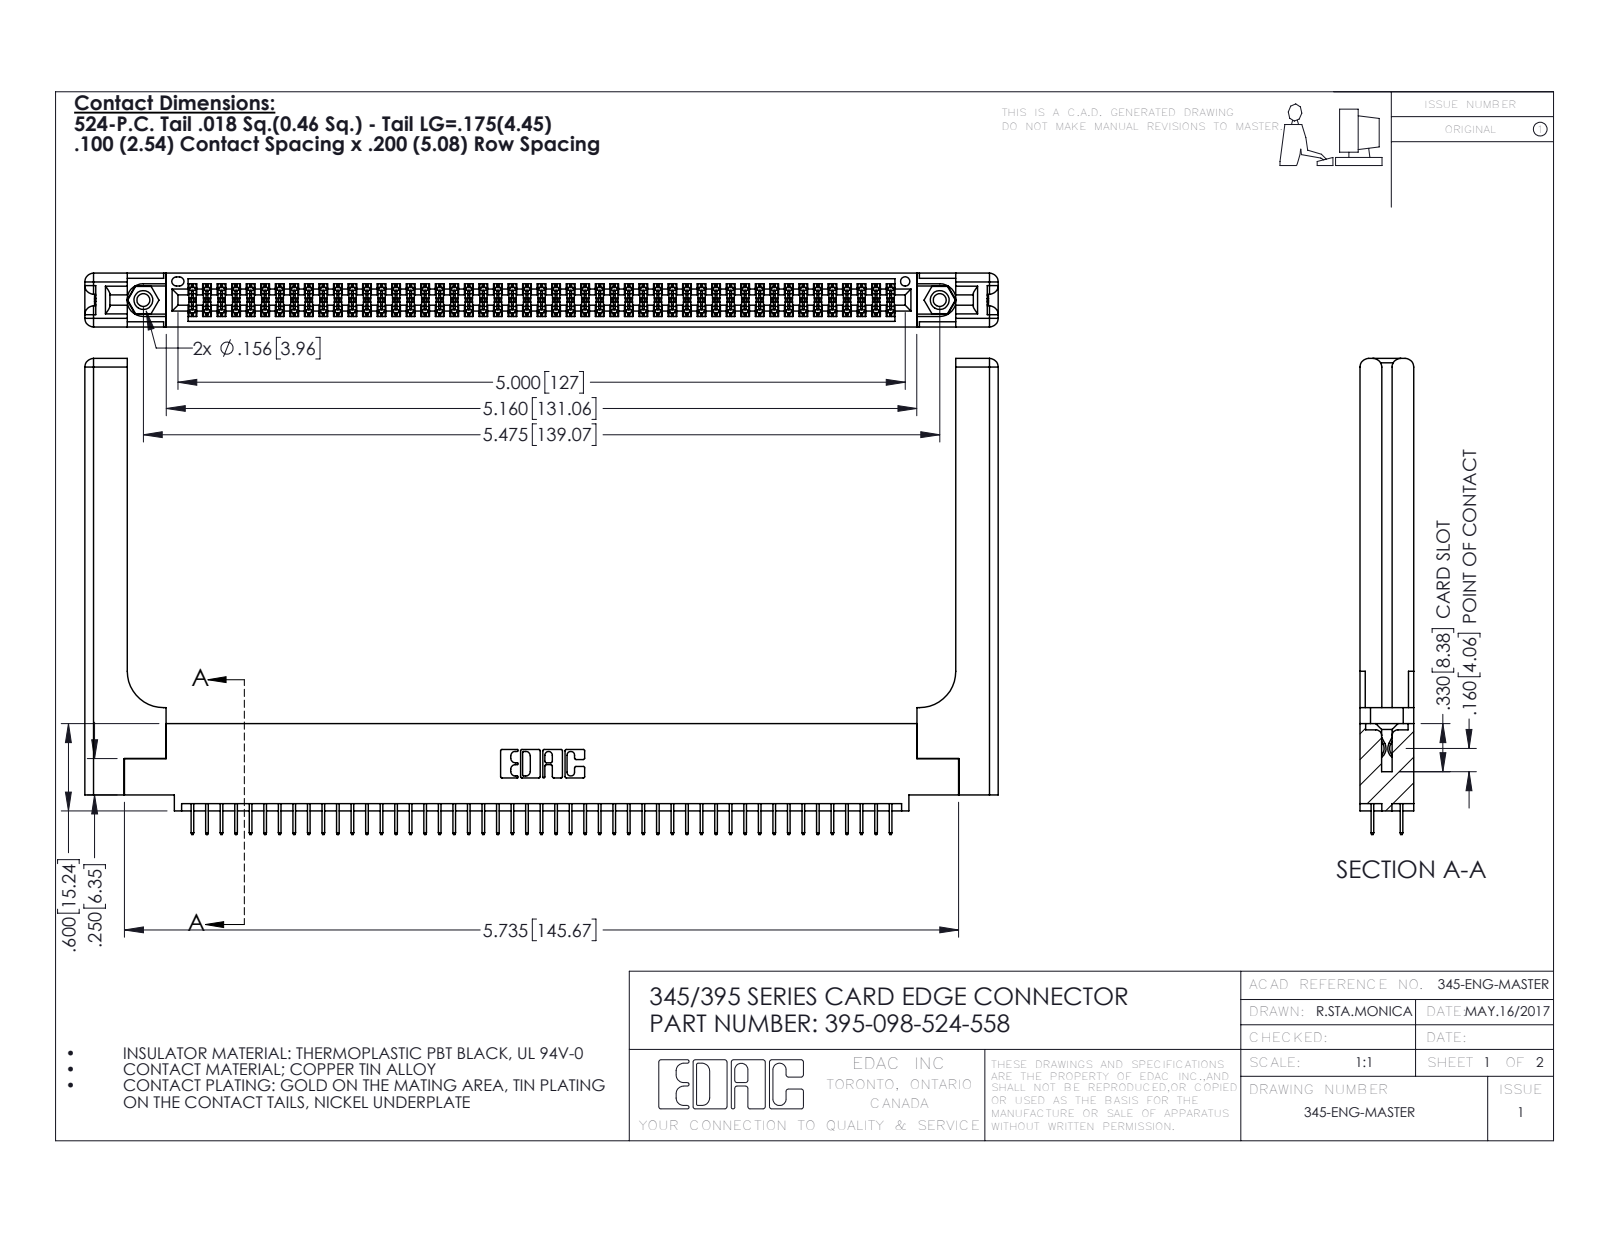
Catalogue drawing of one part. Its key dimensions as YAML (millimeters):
part_name: "395-098-524-558; 345-250-001_345-250-001-102; 345 Part_0.110 Offset - 0.156 Dia-TH; 345-220-058_345-220-058 (+1 more)"
step_written_by: "SolidWorks 2016 (CONFIG_CONTROL_DESIGN)"
units: millimeters
bodies: {solids: 103, faces: 5678, planar: 4054, cylindrical: 1564, other: 60}
overall_size: [159.5, 83.1, 9.4]
volume: 23810
surface_area: 27570
round_holes:
  - {diameter: 2.3, count: 2}
  - {diameter: 3.2, count: 2}
  - {diameter: 4, count: 2}
  - {diameter: 1.6, count: 1}
round_bosses_or_shafts:
  - {diameter: 3.9, count: 2}
partial_cylinders:
  - {radius: 0.2, count: 147}
  - {radius: 0.3, count: 22}
  - {radius: 1.5, count: 16}
  - {radius: 0.2, count: 6}
  - {radius: 0.8, count: 6}
  - {radius: 0.7, count: 3}
  - {radius: 0.4, count: 2}
  - {radius: 0.5, count: 2}
face_to_face_distances: [1.8, 9.4, 7.6, 5.1, 2.5, 6.9, 0.6, 5.7, 3.8, 3.8]
hole_center_spacings: [6.9, 133.1, 139.1]
